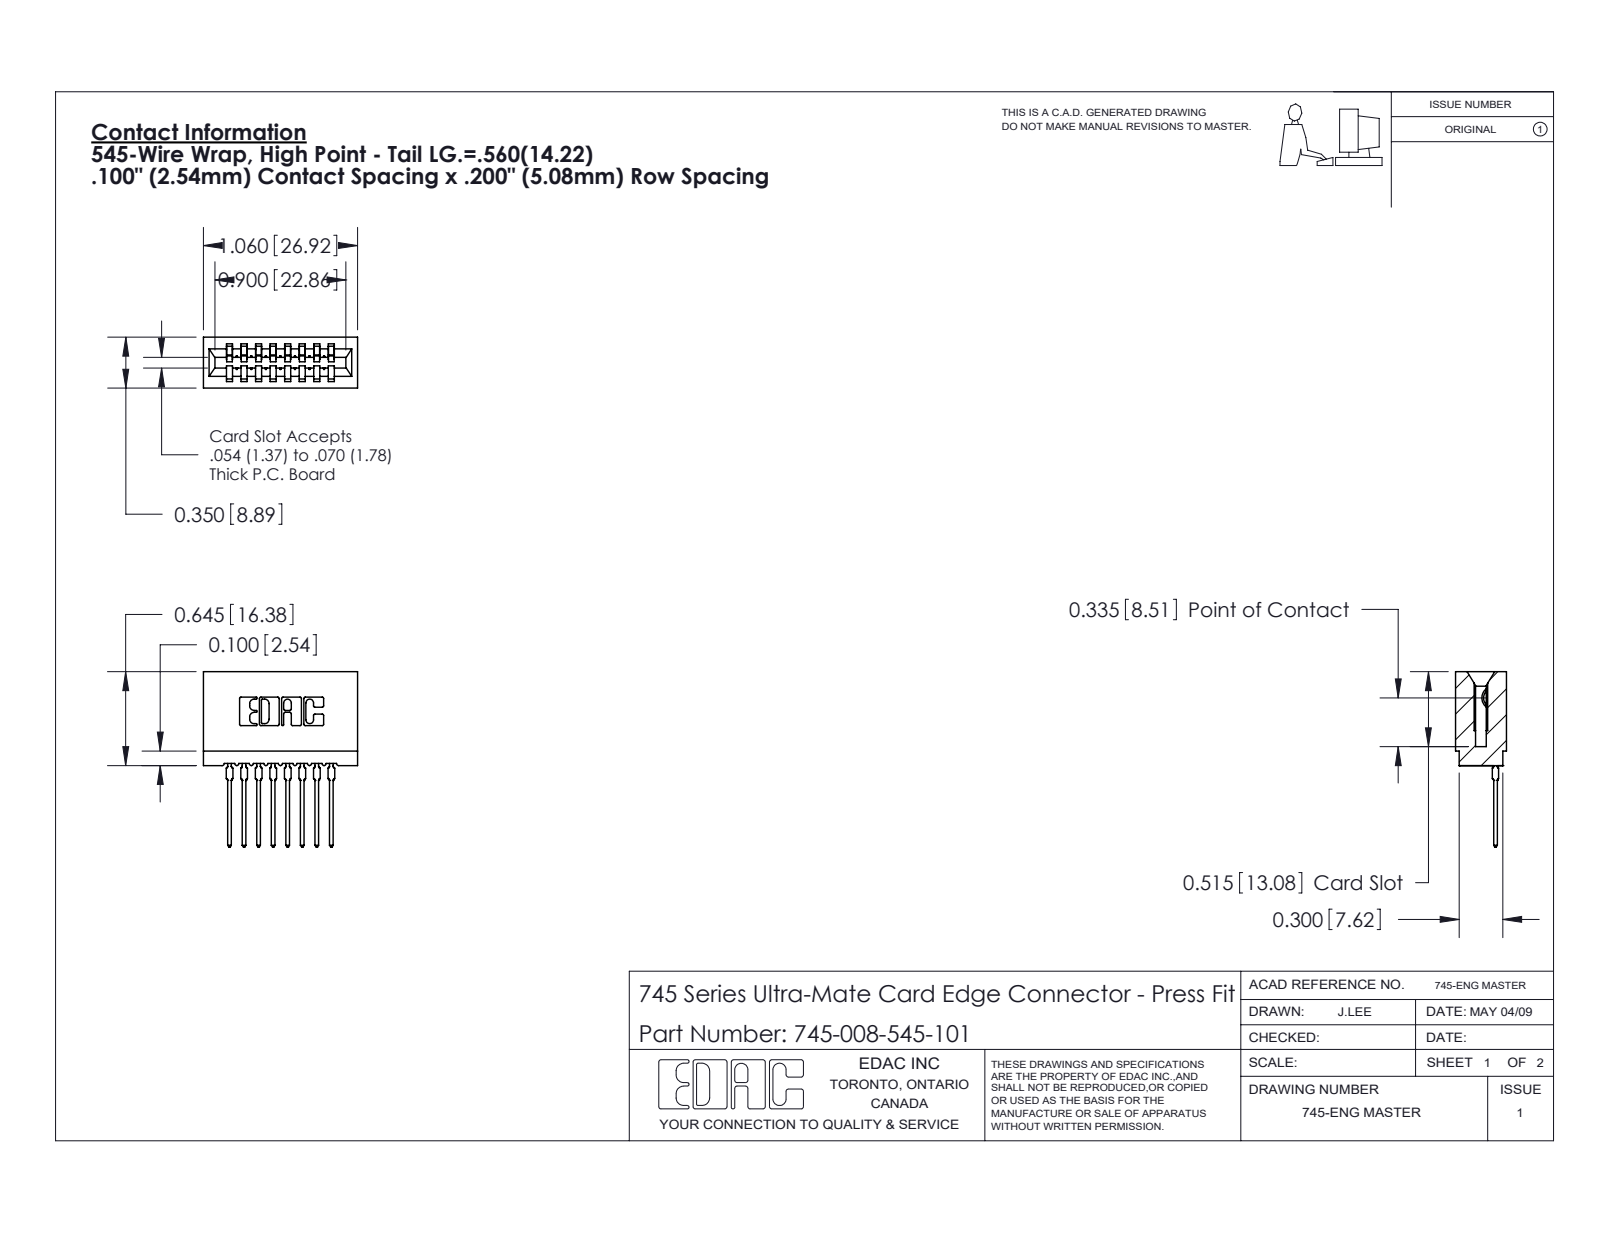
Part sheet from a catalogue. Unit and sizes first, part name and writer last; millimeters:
Units: millimetres
Overall size (bounding box): 30.6 × 26.9 × 8.9
Partial cylindrical surfaces — rounded edges, fillets, slot ends (radius × count): R0.3 ×22, R0.4 ×16, R0.5 ×16, R0.2 ×6, R0.8 ×6, R0.1 ×4, R0.3 ×4, R0.7 ×3
Main face-to-face distances: 2.5, 5.1, 7.6, 1.1, 10.2, 3.6, 1.5, 6.1, 12.7, 4
Volume: 2 570 mm³ · Surface area: 4 255 mm²
Bodies: 9 solids, 991 faces (591 planar, 192 cylindrical, 208 other)
Part name (STEP PRODUCT): 745-008-545-101; 745-292-001_545; 745 Part_Insulator Option - 01
STEP written by: SolidWorks 2020 (CONFIG_CONTROL_DESIGN)
